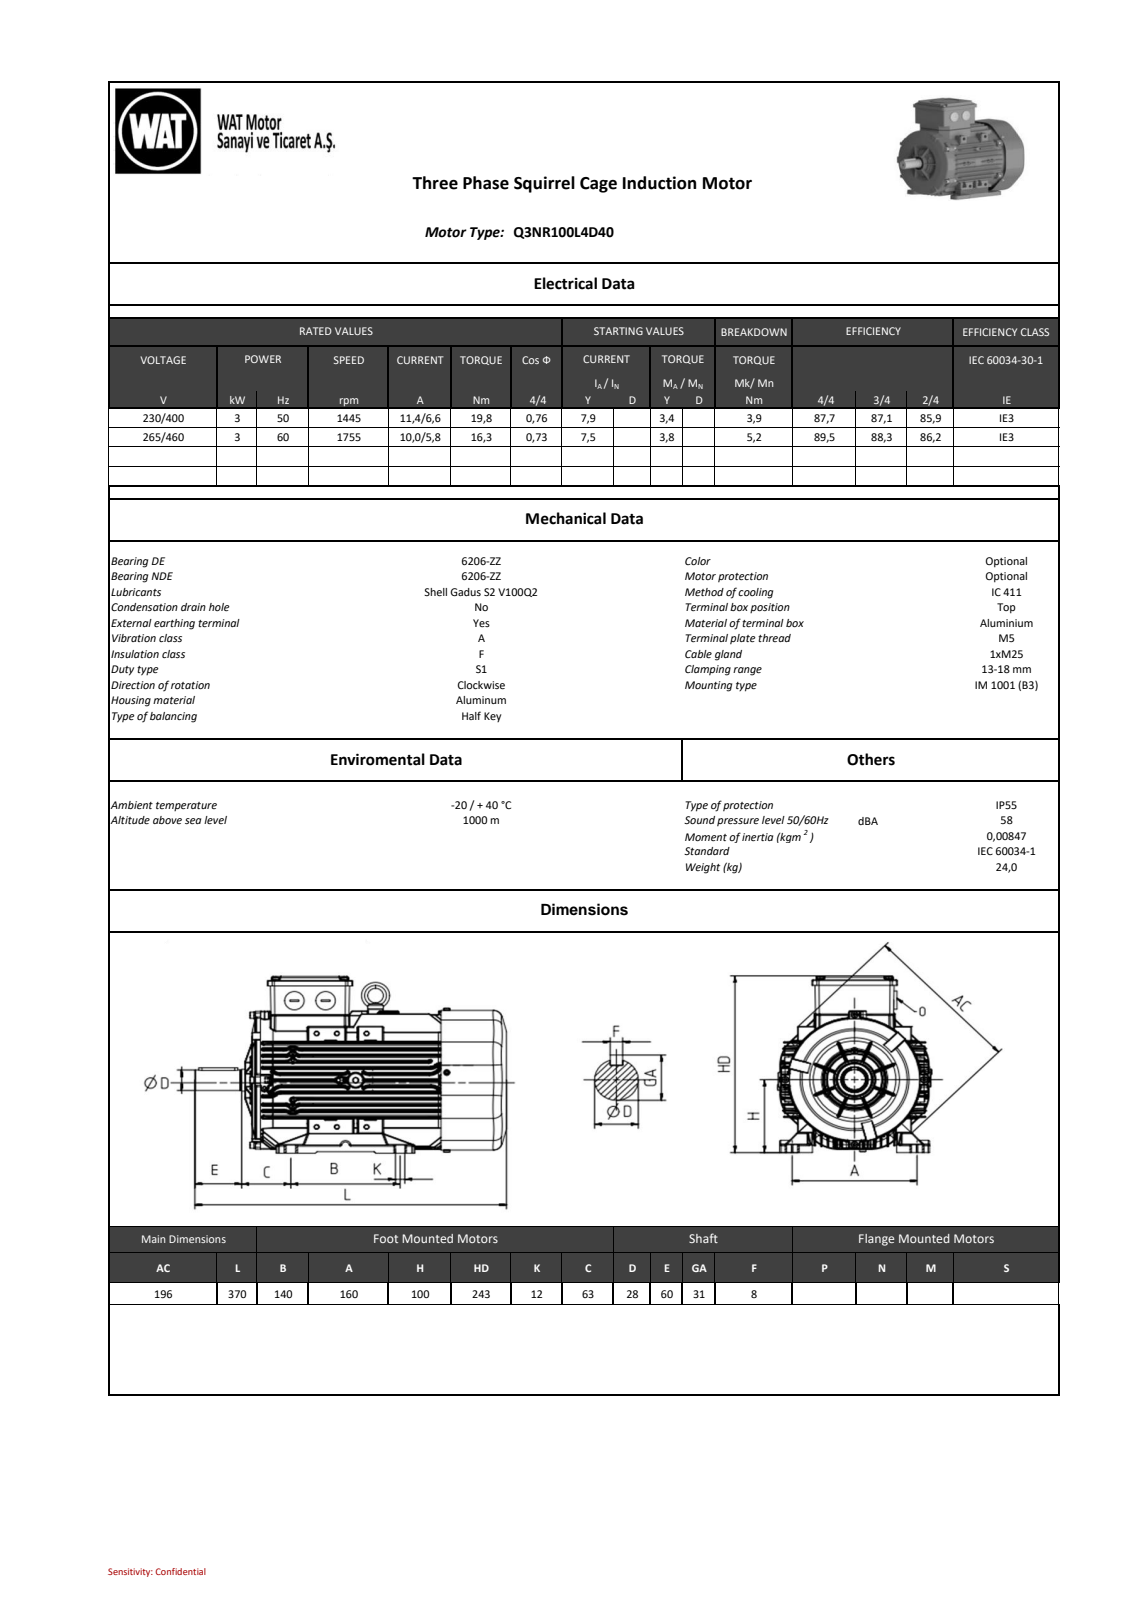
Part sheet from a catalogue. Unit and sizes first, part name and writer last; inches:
Units: inches
Overall size (bounding box): 14.567 × 9.075 × 7.874
Round holes (diameter × count): ⌀0.472 ×2, ⌀0.335 ×1, ⌀0.413 ×1, ⌀1.709 ×1, ⌀1.717 ×1
Round bosses / shafts (diameter × count): ⌀0.315 ×7, ⌀0.236 ×6, ⌀0.394 ×4, ⌀0.465 ×3, ⌀1.094 ×2, ⌀0.994 ×2, ⌀6.89 ×1, ⌀6.732 ×1
Partial cylindrical surfaces — rounded edges, fillets, slot ends (radius × count): R0.02 ×444, R0.031 ×323, R0.039 ×165, R0.03 ×147, R0.059 ×66, R0.157 ×51, R0.01 ×29, R0.079 ×28
Main face-to-face distances: 0.551, 0.031, 0.208, 10.157, 11.772, 1.614, 1.102, 0.118, 0.548, 3.307
Hole centre spacings: 1.535
Bodies: 0 solids, 6436 faces (1663 planar, 2037 cylindrical, 2736 other)
Part name (STEP PRODUCT): C90127E0127Fj6ma
STEP written by: SIEMENS PLM Software NX 11.0 (AUTOMOTIVE_DESIGN)
